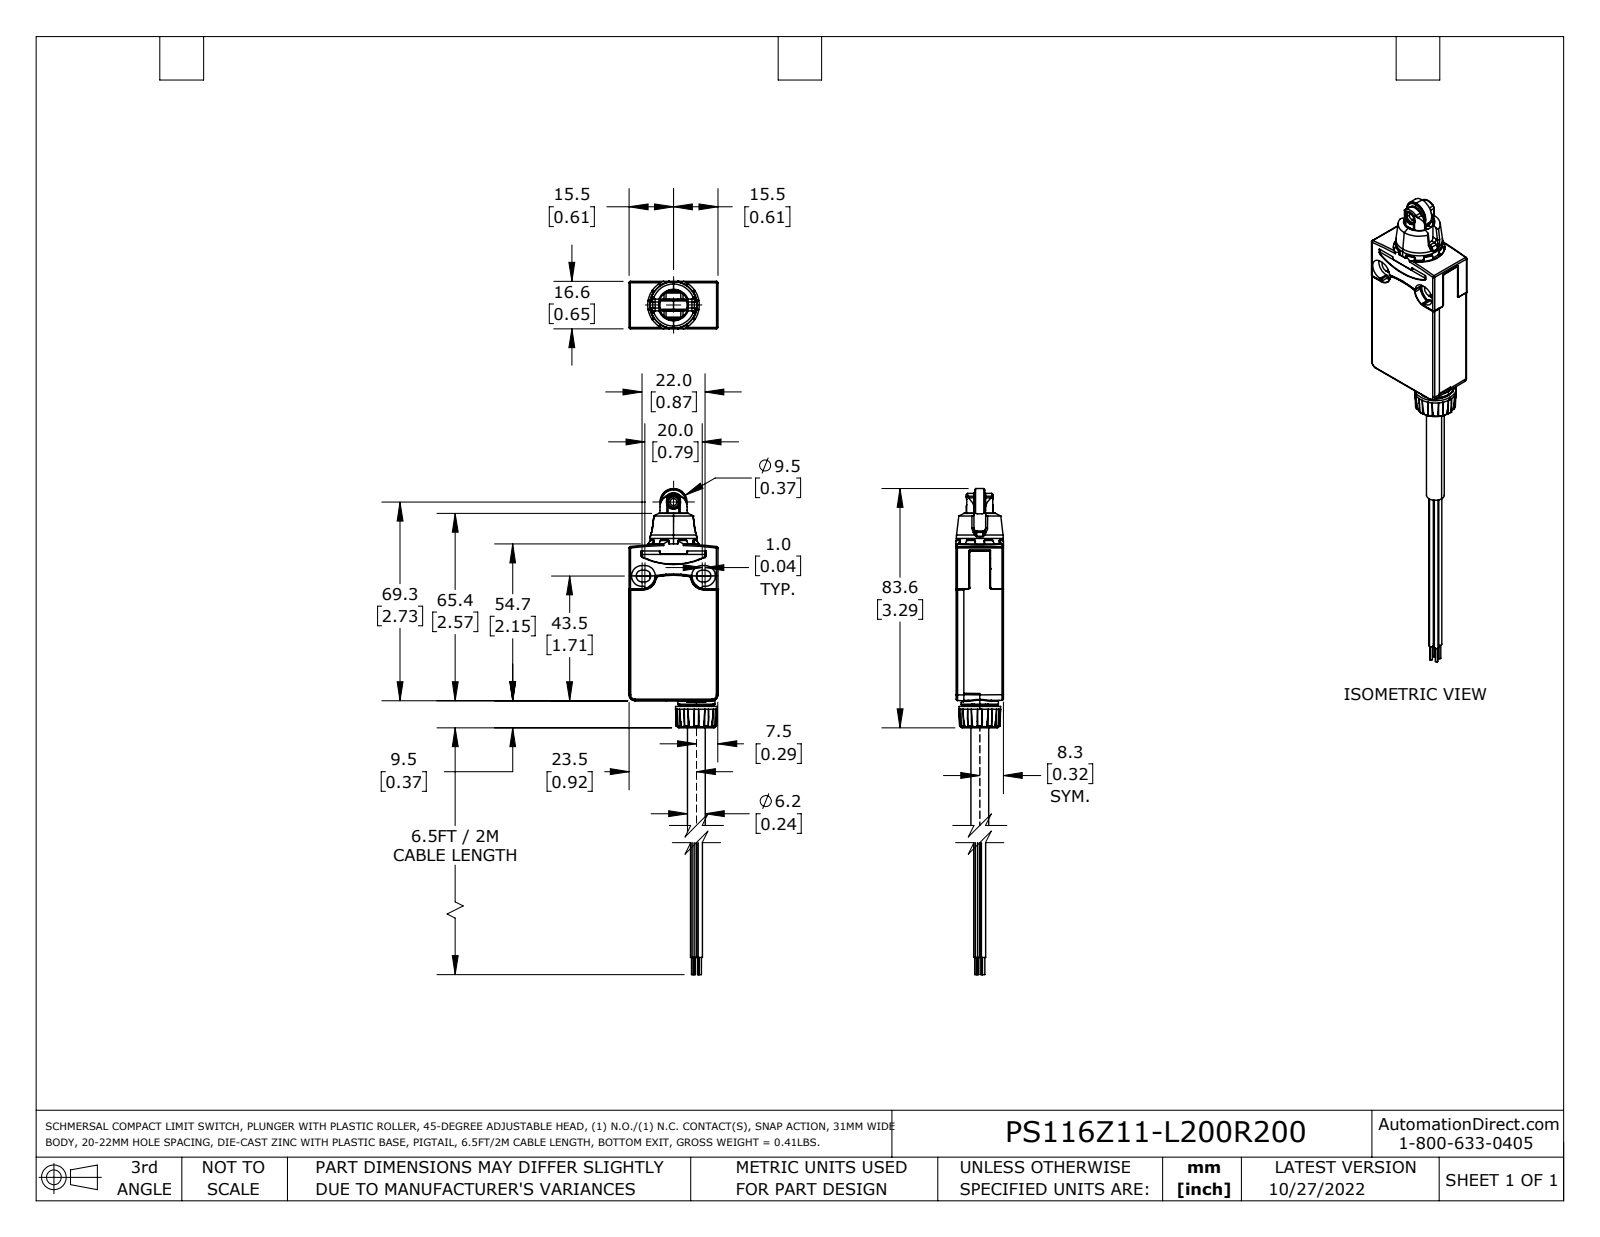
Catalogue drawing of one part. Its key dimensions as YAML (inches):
part_name: "PS116Z11-L200R200_Default"
step_written_by: "SolidWorks 2021 (CONFIG_CONTROL_DESIGN)"
units: inches
bodies: {solids: 2, faces: 1214, planar: 350, cylindrical: 504, other: 360}
overall_size: [7.541, 1.22, 0.654]
volume: 1.855
surface_area: 22.67
round_holes:
  - {diameter: 0.079, count: 1}
  - {diameter: 0.094, count: 1}
  - {diameter: 0.124, count: 1}
  - {diameter: 0.138, count: 1}
  - {diameter: 0.197, count: 1}
  - {diameter: 0.252, count: 1}
  - {diameter: 0.264, count: 1}
  - {diameter: 0.457, count: 1}
  - {diameter: 0.48, count: 1}
  - {diameter: 0.571, count: 1}
round_bosses_or_shafts:
  - {diameter: 0.059, count: 4}
  - {diameter: 0.031, count: 4}
  - {diameter: 0.512, count: 2}
  - {diameter: 0.646, count: 1}
  - {diameter: 0.571, count: 1}
  - {diameter: 0.567, count: 1}
  - {diameter: 0.524, count: 1}
  - {diameter: 0.449, count: 1}
partial_cylinders:
  - {radius: 0.008, count: 144}
  - {radius: 0.004, count: 73}
  - {radius: 0.02, count: 38}
  - {radius: 0.039, count: 22}
  - {radius: 0.014, count: 10}
  - {radius: 0.012, count: 6}
  - {radius: 0.079, count: 5}
  - {radius: 0.081, count: 4}
face_to_face_distances: [0.65, 0.652, 1.22, 0.067, 0.118, 0.116, 0.654, 0.138, 0.22, 0.041]
hole_center_spacings: [0.315]
